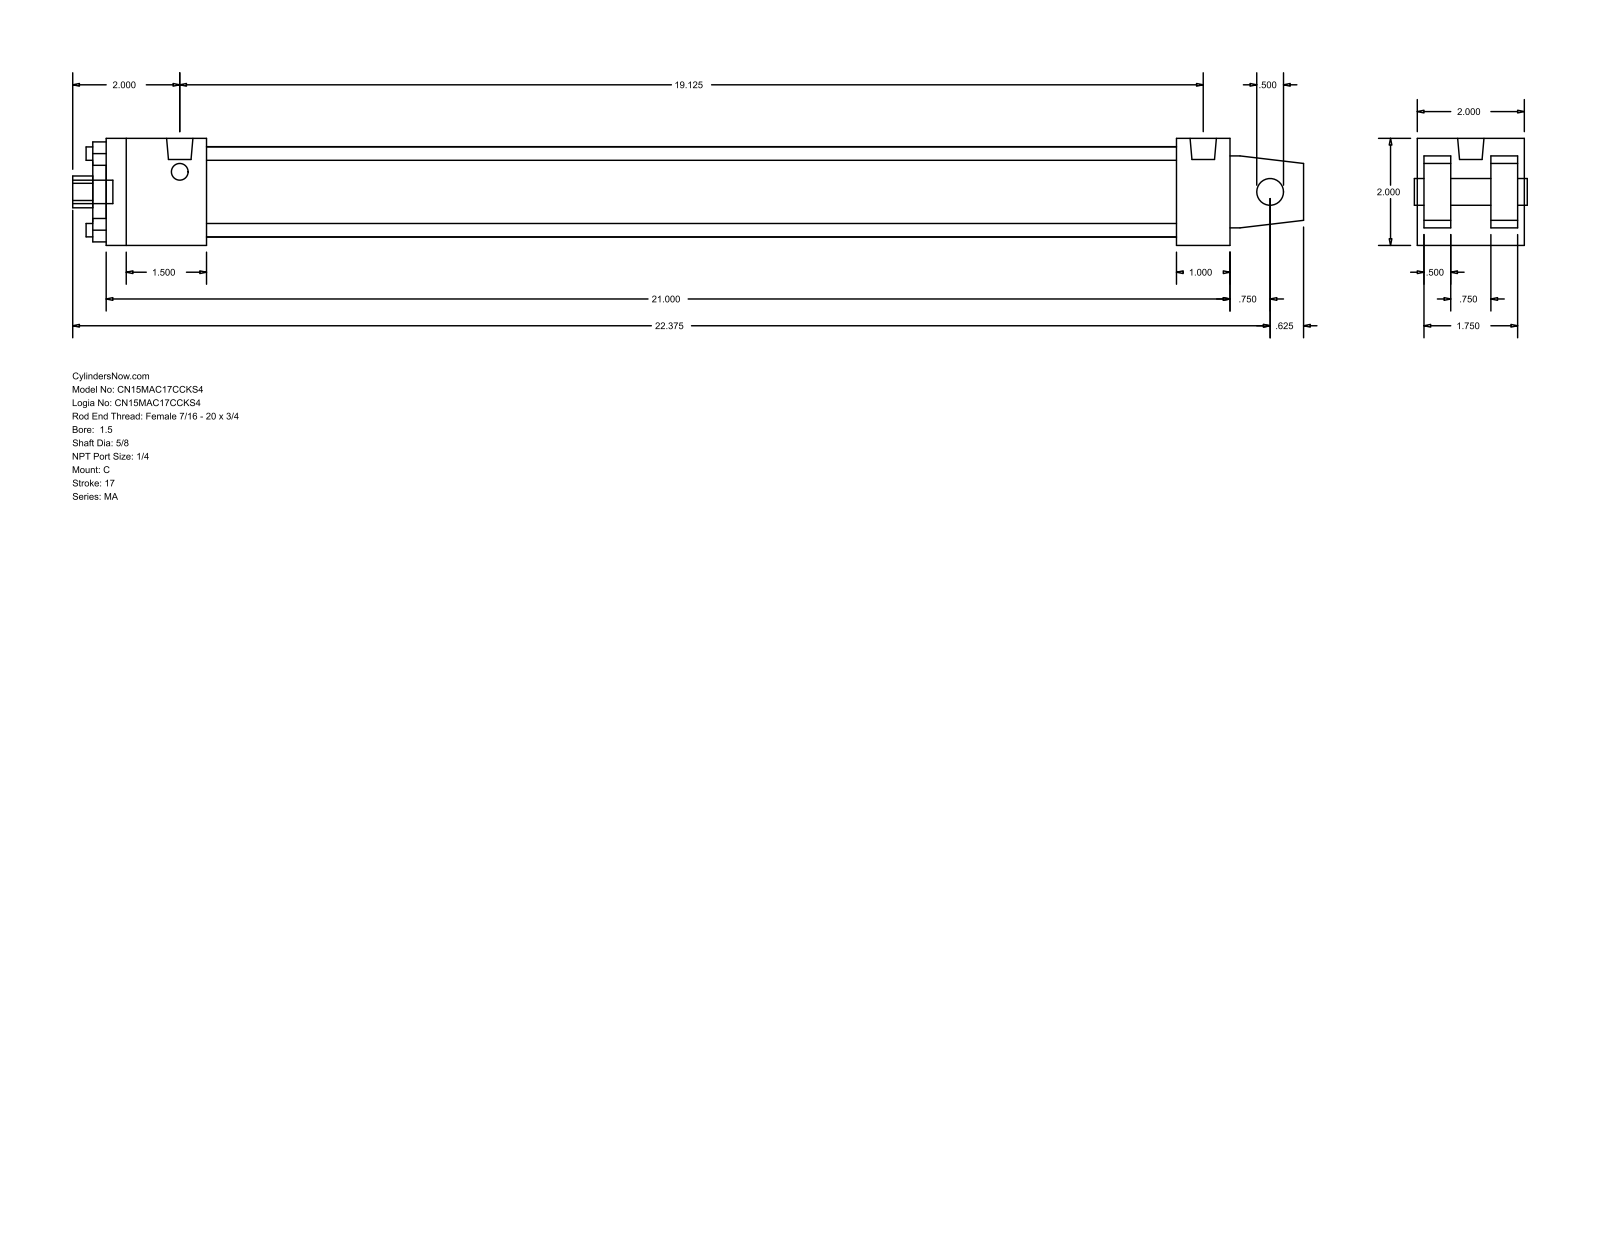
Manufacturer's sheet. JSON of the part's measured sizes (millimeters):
{"part_name": "MA_C__0150_0.625", "step_written_by": "GSSL Pune (CONFIG_CONTROL_DESIGN)", "units": "millimeters", "bodies": {"solids": 0, "faces": 103, "planar": 76, "cylindrical": 27, "other": 0}, "overall_size": [584.2, 50.8, 50.8], "round_holes": [[6.35, 4], [12.7, 1], [15.88, 1], [28.57, 1], [42.93, 1]], "round_bosses_or_shafts": [[7.94, 4], [12.49, 2], [11.11, 1]], "partial_cylinders_radius": [[7.54, 1]], "face_to_face_distances": [50.8, 34.93, 12.7, 3.17, 15.87, 47.63, 31.76, 533.39, 508, 25.39], "hole_center_spacings": [25.68, 36.32, 51.36]}
